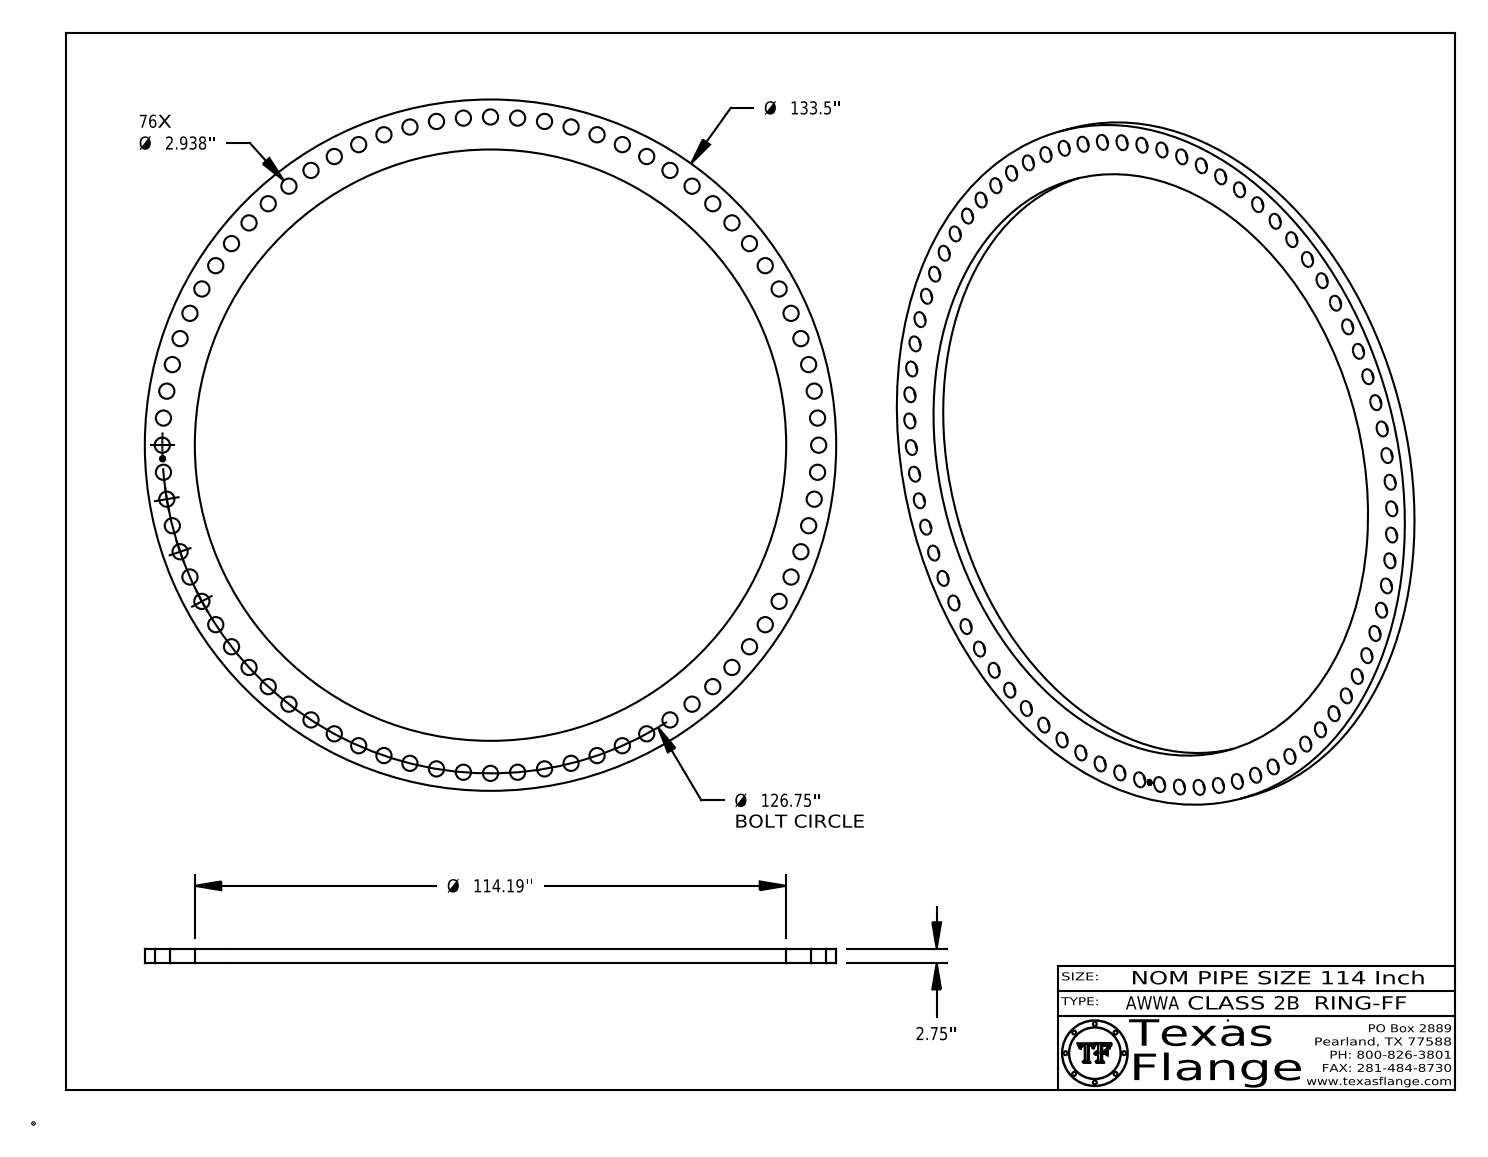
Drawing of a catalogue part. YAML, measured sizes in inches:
part_name: "AWWA Class 2B-RING-FF"
step_written_by: "CATIA V5 STEP AP214 (AUTOMOTIVE_DESIGN)"
units: inches
bodies: {solids: 1, faces: 543, planar: 367, cylindrical: 176, other: 0}
overall_size: [133.5, 133.5, 2.75]
volume: 8913
surface_area: 10552
round_holes:
  - {diameter: 2.938, count: 76}
  - {diameter: 1, count: 1}
  - {diameter: 114.19, count: 1}
round_bosses_or_shafts:
  - {diameter: 0.061, count: 8}
  - {diameter: 133.5, count: 1}
  - {diameter: 0.788, count: 1}
face_to_face_distances: [2.75, 2.735, 0.015, 0.298, 0.293, 0.019, 0.055, 0.193, 0.248, 0.044]
hole_center_spacings: [10.467, 5.238, 31.115, 50.915, 15.678, 26.011, 60.326, 63.375]
